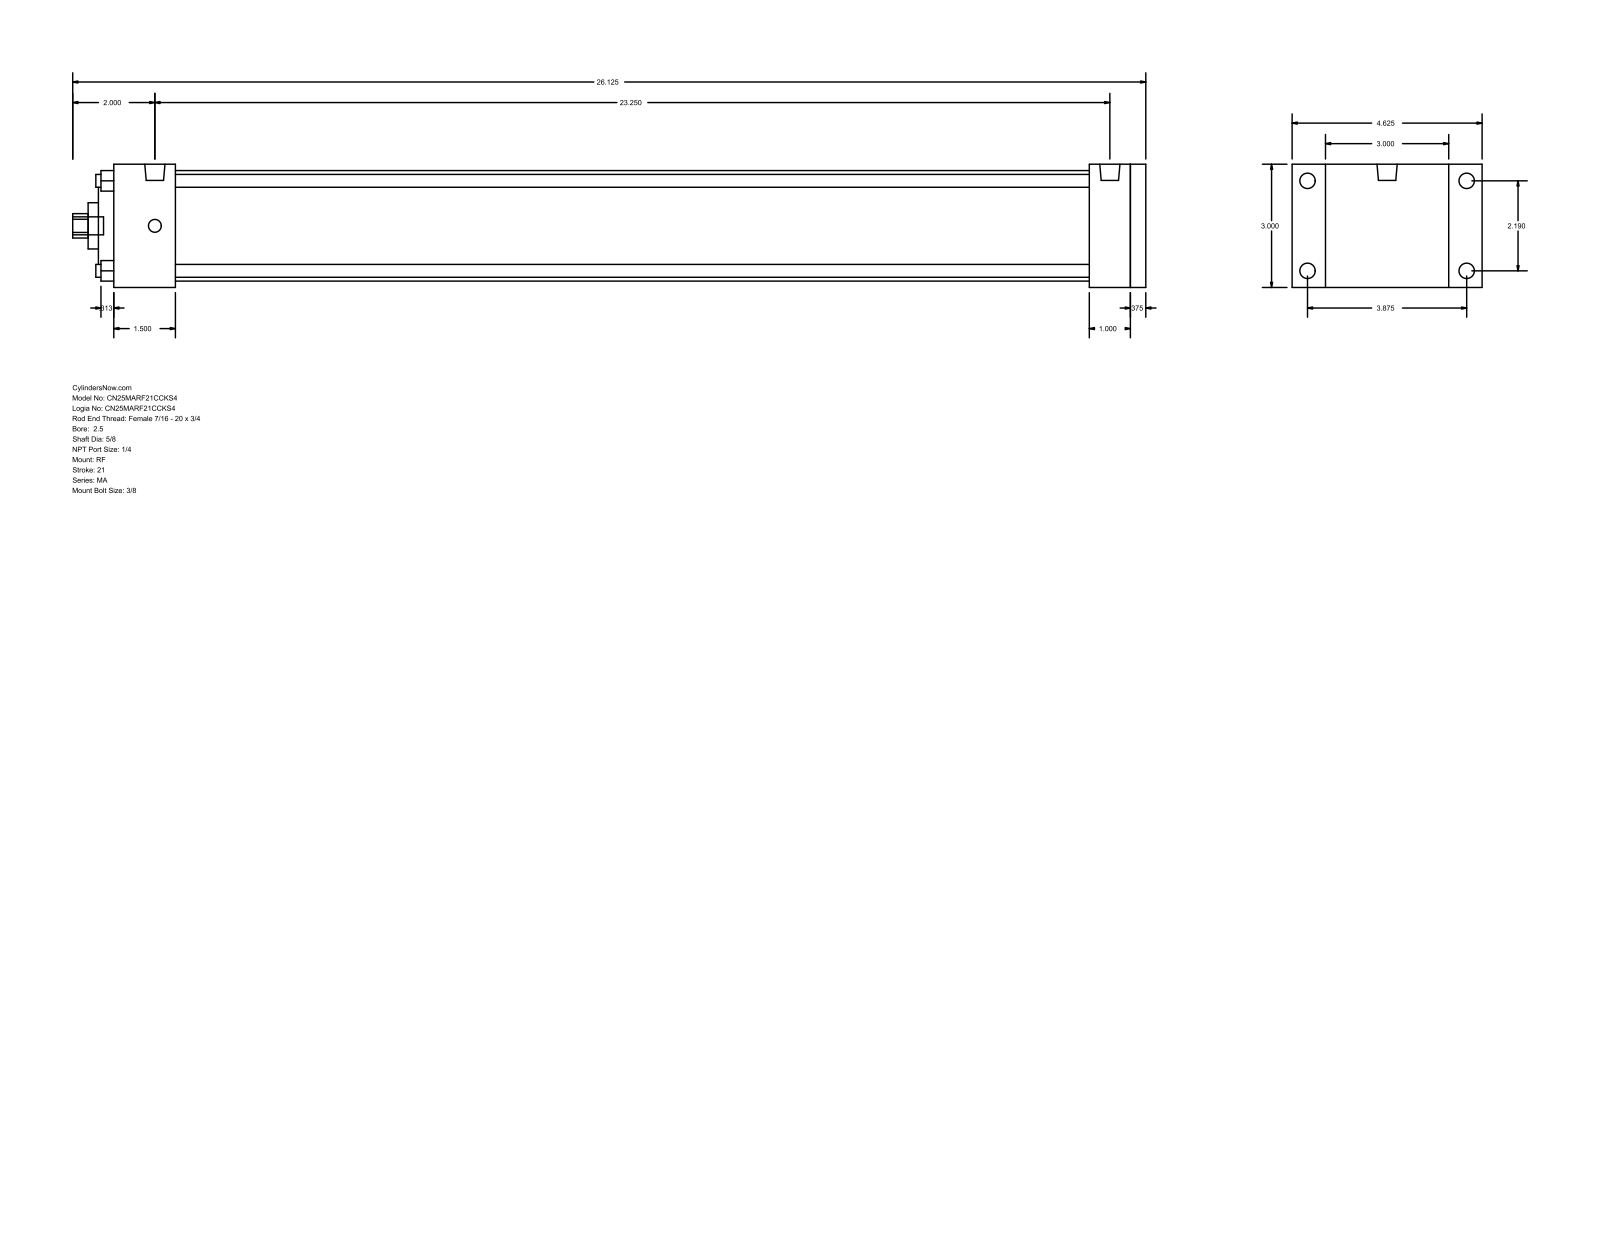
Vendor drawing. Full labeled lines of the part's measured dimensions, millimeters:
Part name (STEP PRODUCT): MA_RF__0250_0.625
STEP written by: GSSL Pune (CONFIG_CONTROL_DESIGN)
Units: millimetres
Bodies: 0 solids, 94 faces (65 planar, 29 cylindrical, 0 other)
Overall size (bounding box): 663.58 × 117.47 × 76.2
Round holes (diameter × count): ⌀7.94 ×4, ⌀15.88 ×1, ⌀28.57 ×1, ⌀50.8 ×1, ⌀68.33 ×1
Round bosses / shafts (diameter × count): ⌀9.53 ×4, ⌀7.94 ×4, ⌀12.49 ×2, ⌀11.11 ×1
Partial cylindrical surfaces — rounded edges, fillets, slot ends (radius × count): R7.54 ×1
Main face-to-face distances: 76.2, 638.18, 9.53, 628.65, 25.4, 38.1, 603.25, 565.15, 590.55, 600.08
Hole centre spacings: 39.33, 55.62, 78.66
